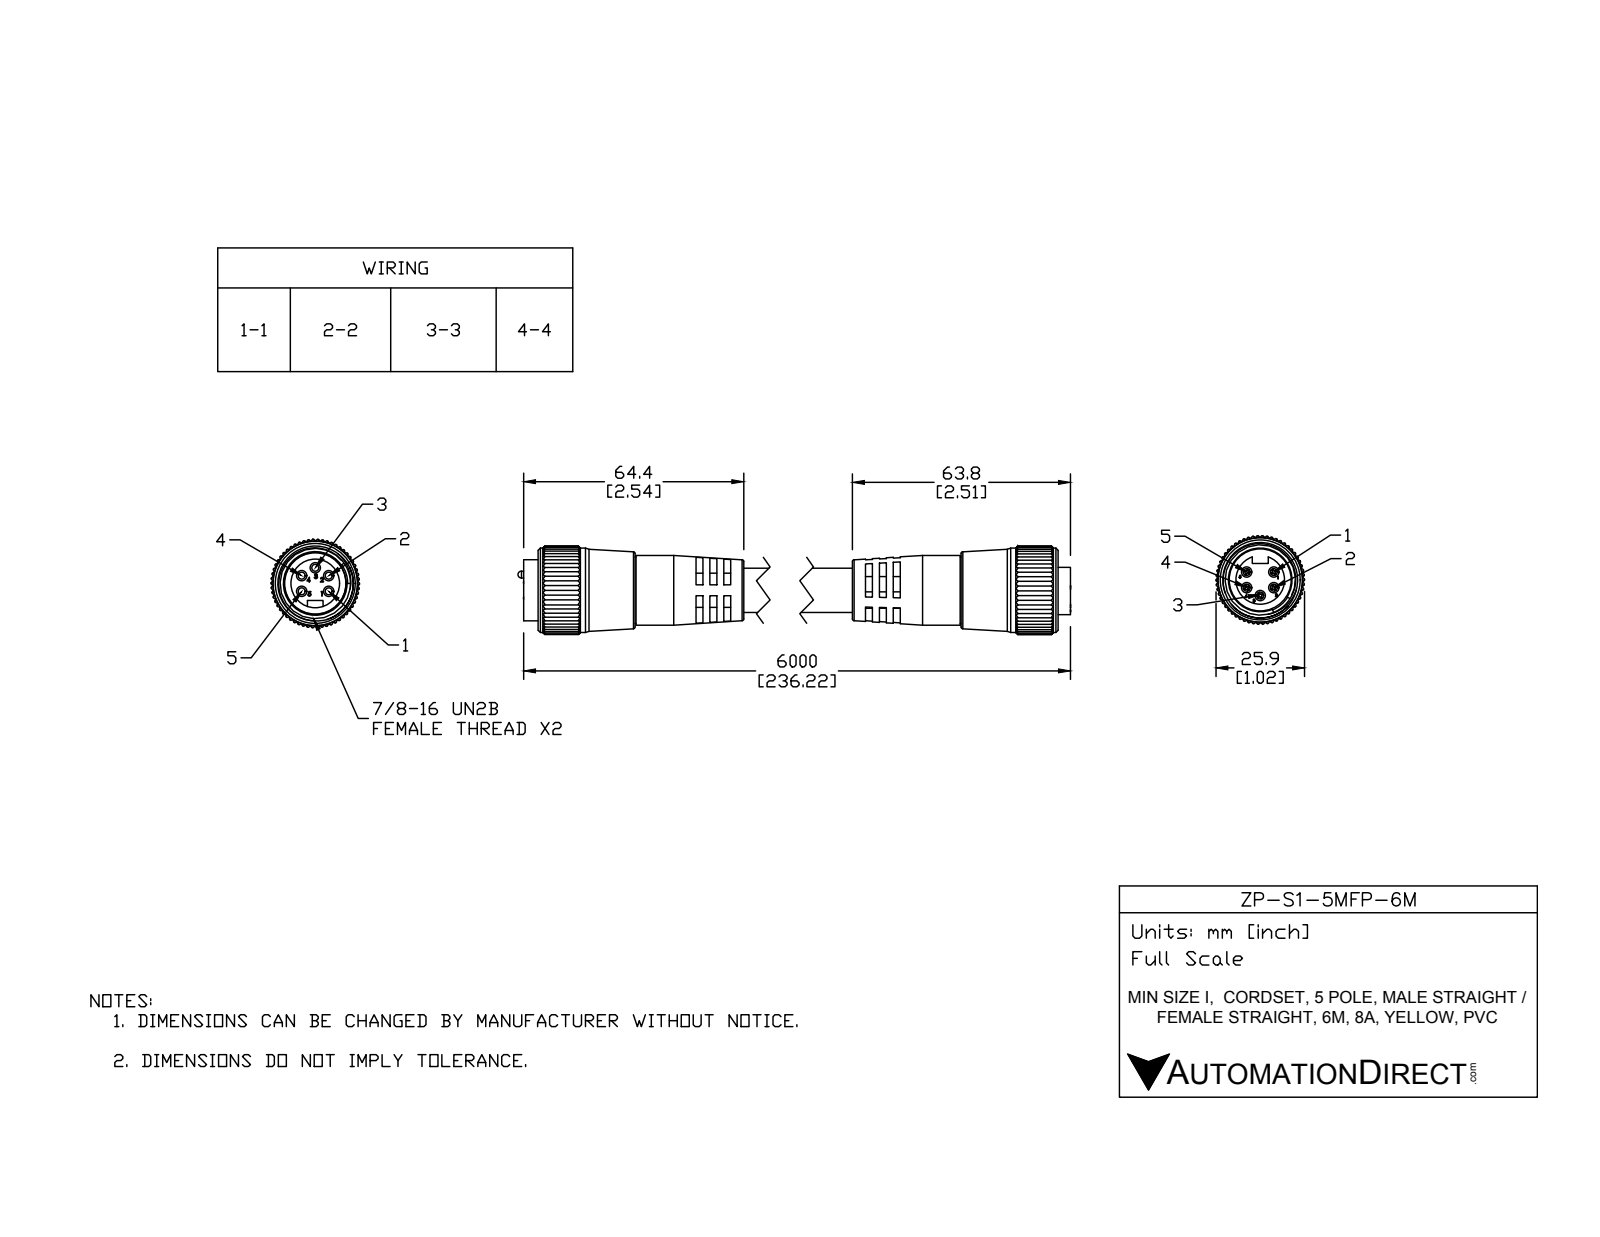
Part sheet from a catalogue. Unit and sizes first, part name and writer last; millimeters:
Units: millimetres
Overall size (bounding box): 229.66 × 25.84 × 25.83
Round holes (diameter × count): ⌀3.05 ×5, ⌀19.96 ×1, ⌀20.45 ×1, ⌀21 ×1
Round bosses / shafts (diameter × count): ⌀2 ×5, ⌀24.68 ×1, ⌀20.4 ×1, ⌀19.5 ×1, ⌀17.88 ×1, ⌀14.22 ×1, ⌀9.91 ×1, ⌀3.05 ×1
Partial cylindrical surfaces — rounded edges, fillets, slot ends (radius × count): R0.25 ×165, R2.29 ×1, R5.25 ×1, R12.93 ×1
Main face-to-face distances: 2, 4.02, 117.68, 113.65, 4.03, 125.74, 59.84, 4.04, 121.7, 121.72
Hole centre spacings: 4.57, 4.56, 7.91, 7.92, 9.14
Volume: 50 854 mm³ · Surface area: 23 442 mm²
Bodies: 9 solids, 1185 faces (439 planar, 630 cylindrical, 116 other)
Part name (STEP PRODUCT): ZP-S1-5MFP-6M
STEP written by: SolidWorks 2015 (AUTOMOTIVE_DESIGN)
